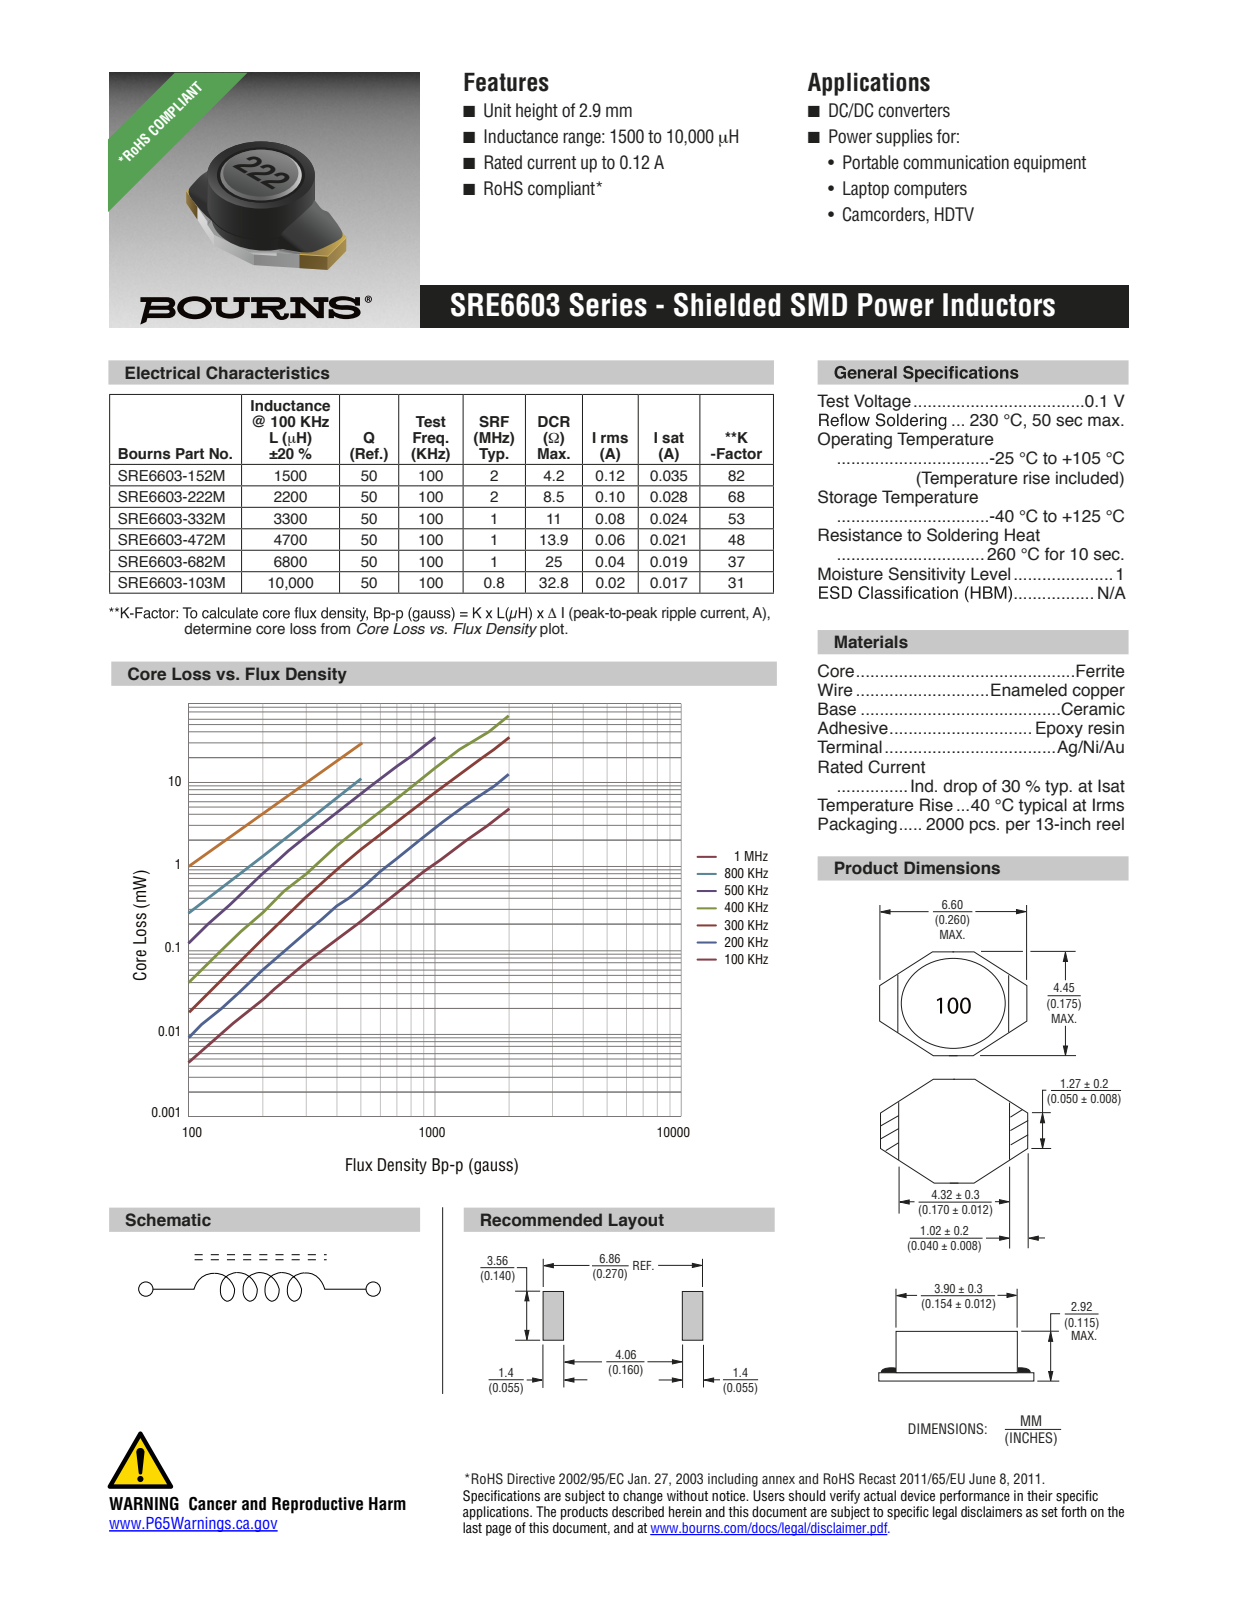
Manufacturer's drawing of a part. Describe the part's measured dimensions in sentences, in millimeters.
The part is named "SRE6603". Its 3-D file was written by "PRO/ENGINEER BY PARAMETRIC TECHNOLOGY CORPORATION, 2010100 (CONFIG_CONTROL_DESIGN)". It is 1 solid with 37 faces: 23 planar, 12 cylindrical and 2 other. Overall it measures 6.6 by 4.45 by 2.92 millimeters. Its volume is 39 cubic millimeters and its surface area 102 square millimeters. Round holes: 1 of diameter 3.44. Round bosses or shafts: 1 of diameter 3.9, 1 of diameter 3.2. Partial cylindrical surfaces (rounded edges, fillets, slot ends): 4 of radius 0.5. The main face-to-face distances are 2.92, 0.5, 2.42, 4.48, 1, 1.92, 1.42, 6.6, 4.46, 1.32.
